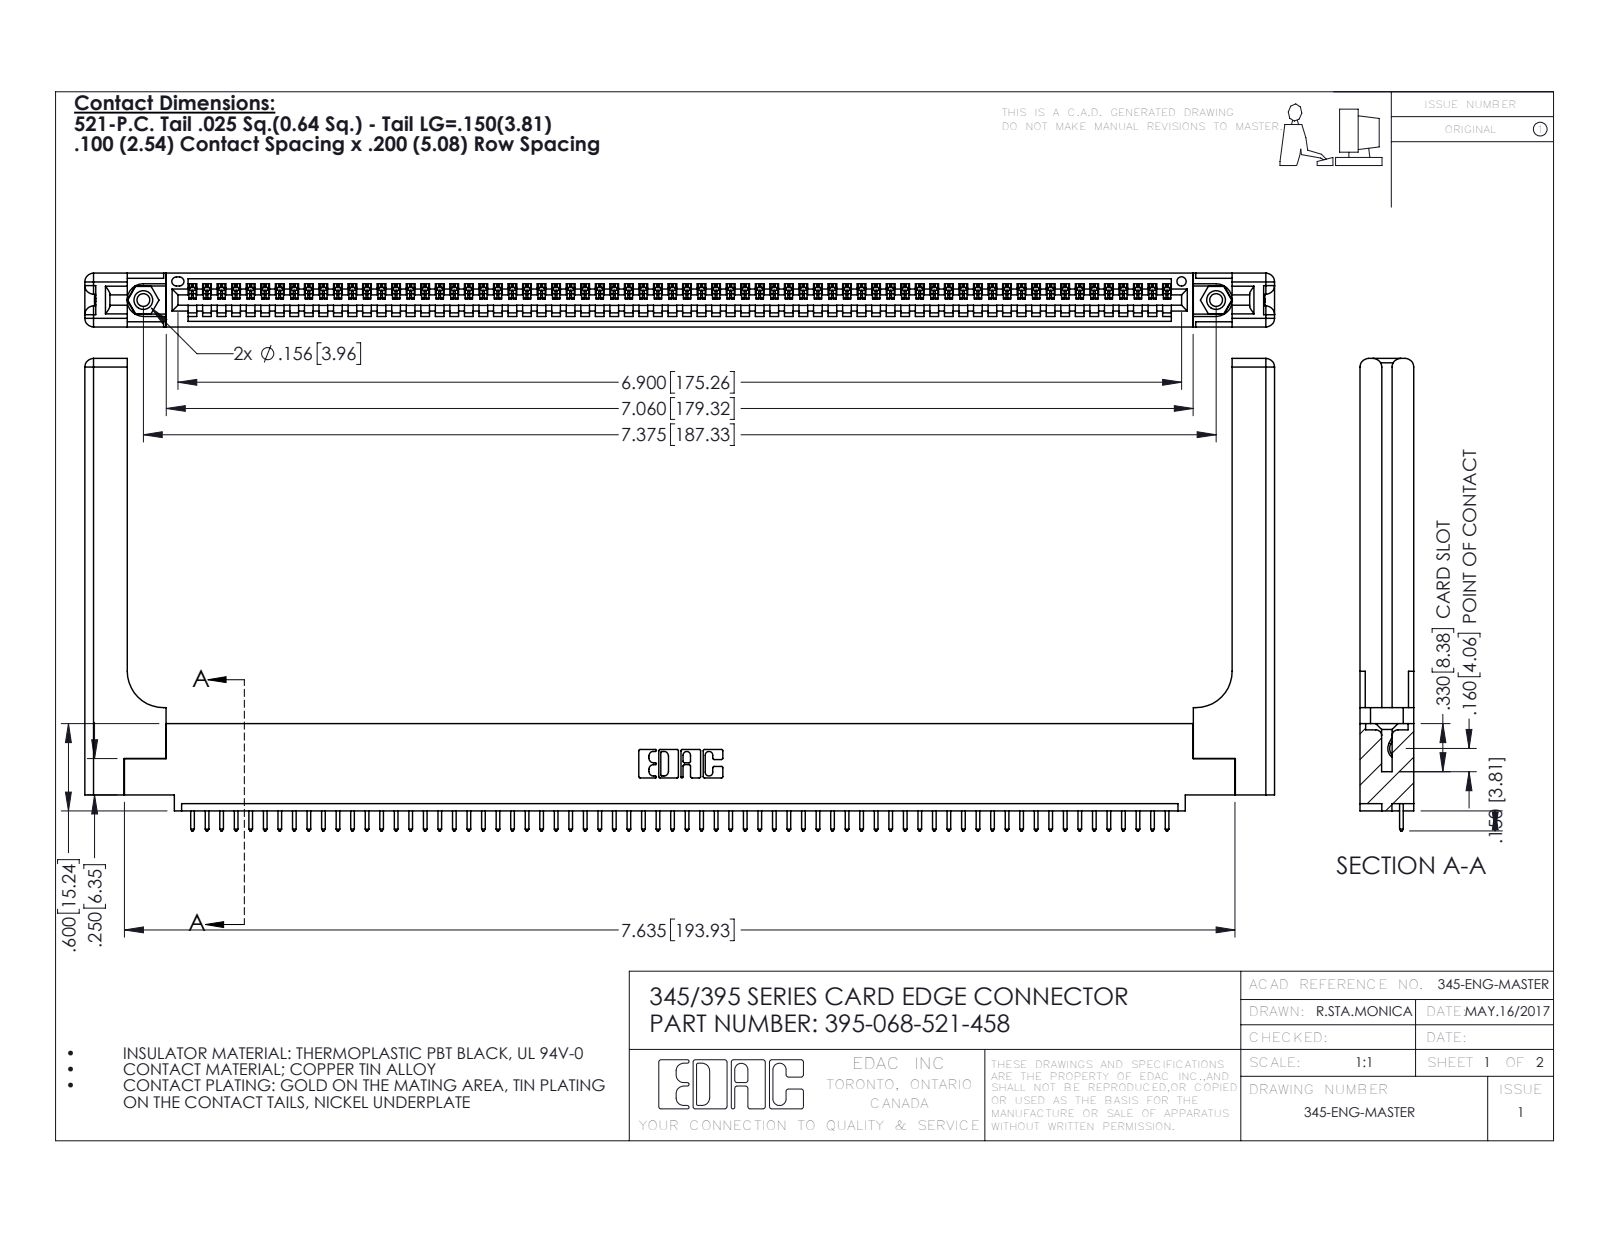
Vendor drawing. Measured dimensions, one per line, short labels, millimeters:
name: 345-292-001_345-293-121; 345 Part_0.110 Offset - 0.156 Dia-TH; 345-250-001_345-250-001-102; 395-068-521-458 (+1 more)
written by: SolidWorks 2016 (CONFIG_CONTROL_DESIGN)
unit: mm
bodies: 73 solids, 4330 faces (2952 planar, 1318 cylindrical, 60 other)
size: 207.7 × 82.5 × 9.4
volume: 28 190 mm³; area: 31 140 mm²
holes: 2× ⌀2.3, 2× ⌀3.2, 2× ⌀4, 1× ⌀1.6
bosses: 2× ⌀3.9
rounds: 136× R0.2, 136× R0.3, 22× R0.3, 16× R1.5, 6× R0.2, 6× R0.8, 3× R0.7, 2× R0.8
face distances: 1.8, 9.4, 7.6, 2.5, 6.9, 0.6, 5.1, 5.7, 3.8, 3.8
hole spacings: 6.9, 181.3, 187.3
